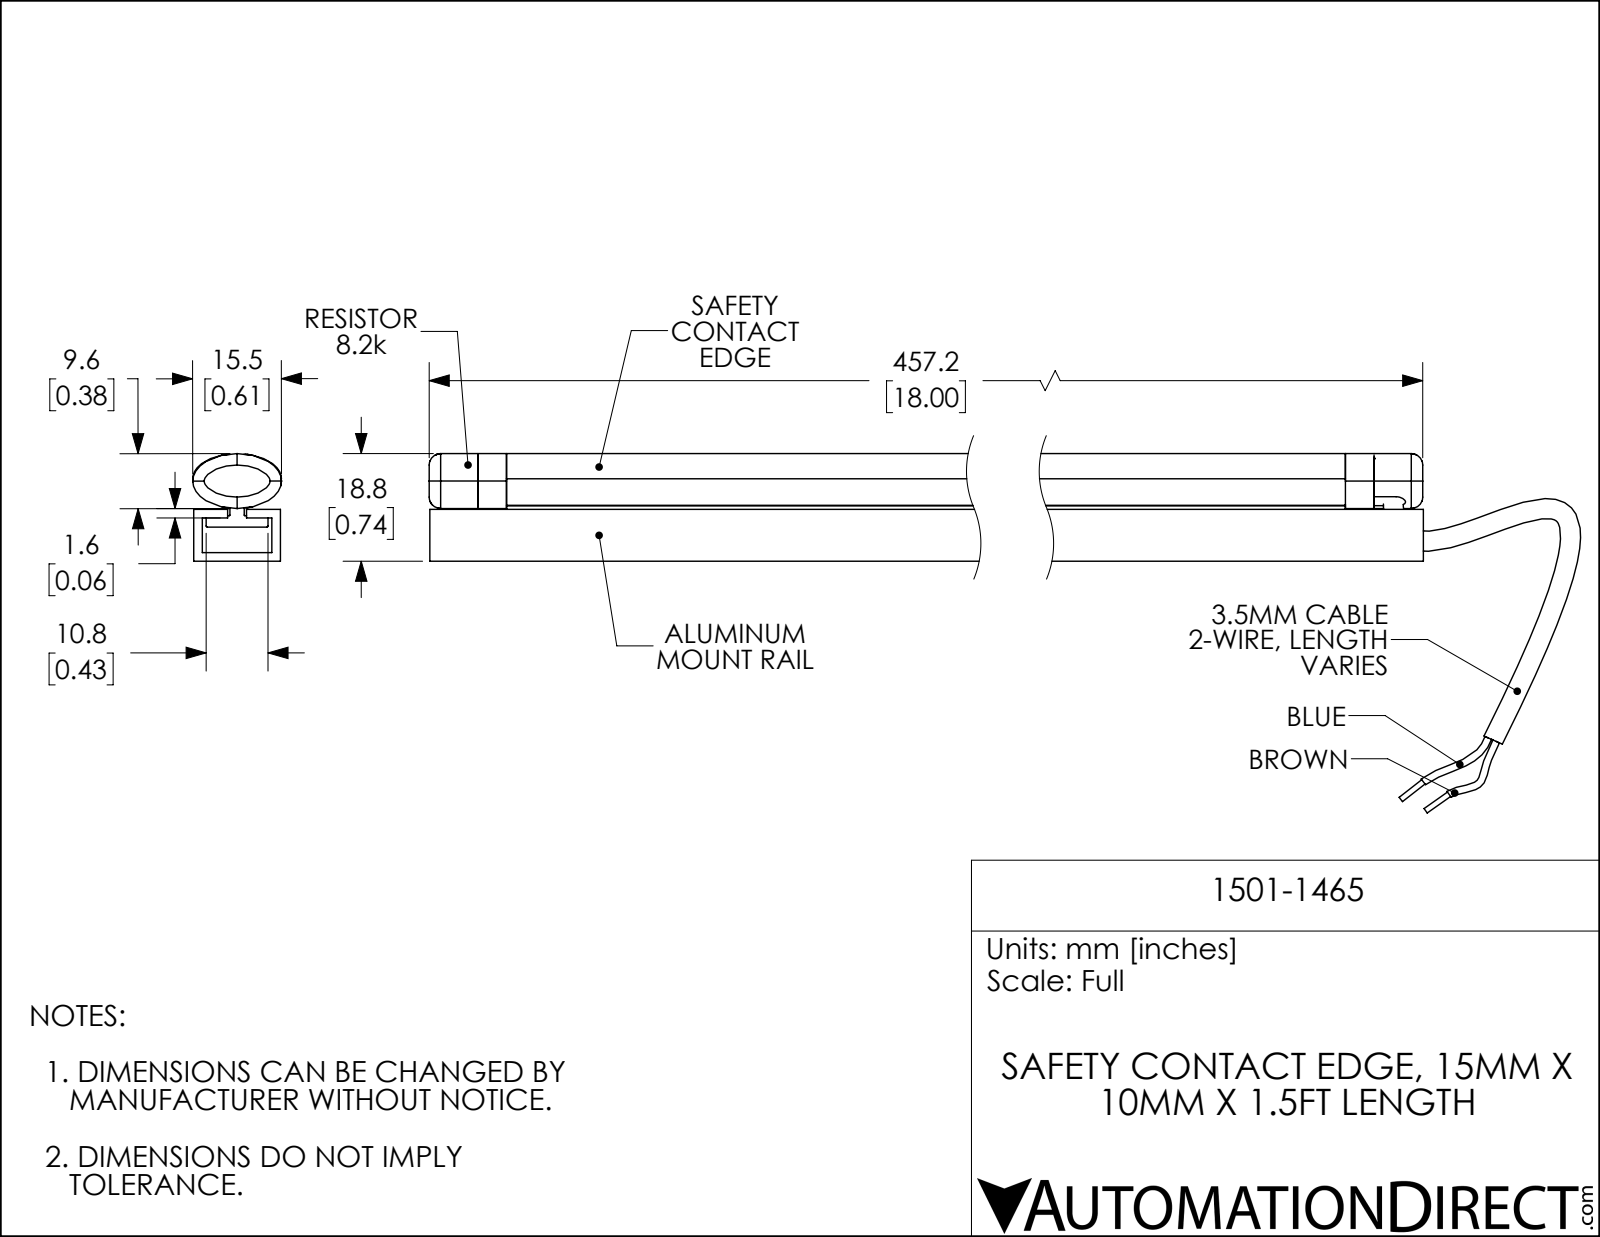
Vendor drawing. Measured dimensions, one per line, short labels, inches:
name: 1501-1465
written by: SolidWorks 2018 (AUTOMOTIVE_DESIGN)
unit: in
bodies: 7 solids, 607 faces (129 planar, 154 cylindrical, 324 other)
size: 19.085 × 2.47 × 0.611
volume: 4.483 in³; area: 128.5 in²
holes: 4× ⌀0.047
bosses: 2× ⌀0.037
rounds: 52× R0.004, 15× R0.016, 10× R0.012, 7× R0.008, 4× R0.02, 4× R0.512, 3× R0.008, 3× R0.059
face distances: 0.059, 0.297, 0.537, 0.356, 0.016, 0.122, 0.234, 0.175, 0.596, 0.238
hole spacings: 0.197, 0.196, 0.197
